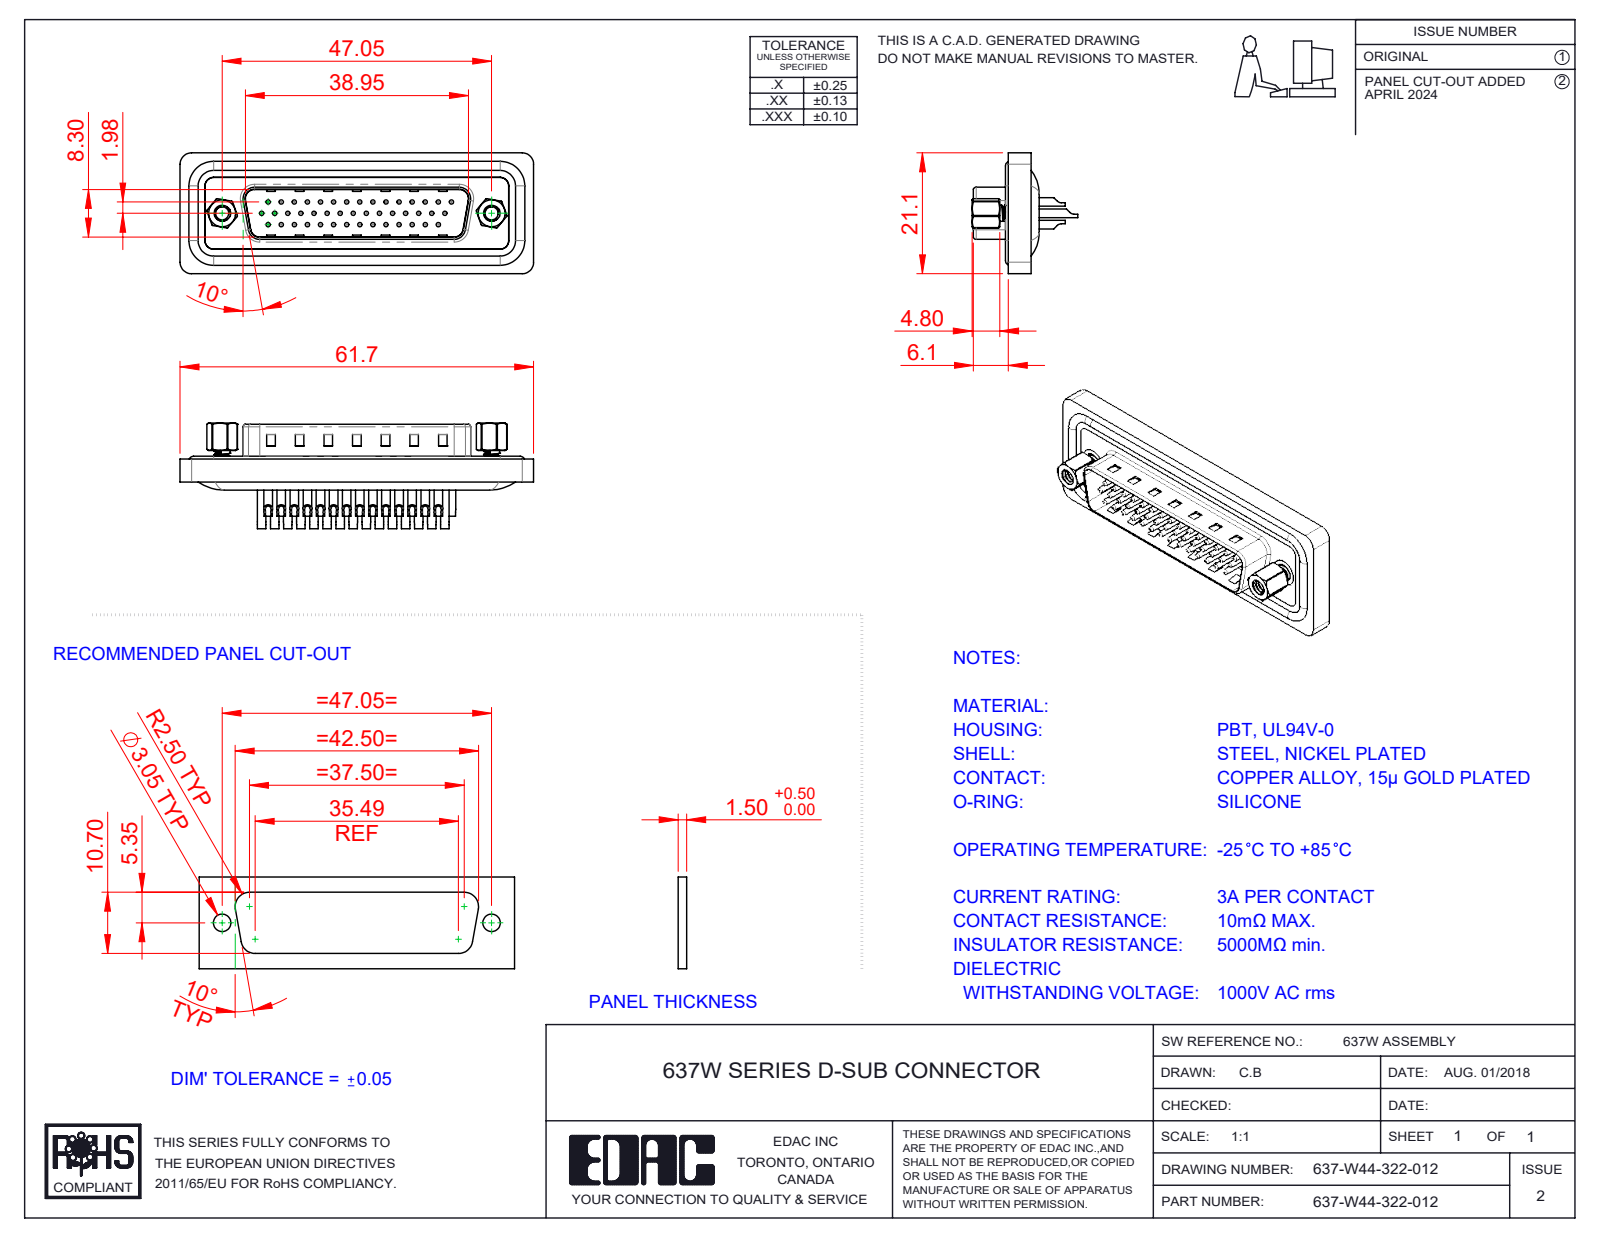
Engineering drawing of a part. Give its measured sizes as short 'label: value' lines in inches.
name: 637W Contact Row 3_22; 637W Contact Row 2_22; 637W Contact Row 1_22; 637W Shell_44 Contacts (+5 more)
written by: SolidWorks 2016 (CONFIG_CONTROL_DESIGN)
unit: in
bodies: 52 solids, 2234 faces (601 planar, 1008 cylindrical, 625 other)
size: 2.431 × 0.831 × 0.719
volume: 0.398 in³; area: 19.49 in²
holes: 44× ⌀0.03, 44× ⌀0.039, 44× ⌀0.059, 44× ⌀0.063, 44× ⌀0.079, 2× ⌀0.089, 2× ⌀0.09, 2× ⌀0.157, 2× ⌀0.189, 2× ⌀0.197
bosses: 21× ⌀0.059, 4× ⌀0.063, 2× ⌀0.193, 2× ⌀0.11, 1× ⌀0.197
rounds: 14× R0.079, 13× R0.059, 8× R0.02, 6× R0.106, 4× R0.035, 4× R0.063, 4× R0.169, 3× R0.039
face distances: 0.016, 0.063, 0.098, 0.114, 0.043, 0.222, 0.608, 0.03, 0.252, 0.579
hole spacings: 0.09, 0.156, 0.09, 0.18, 0.324, 0.27, 0.45, 0.59
